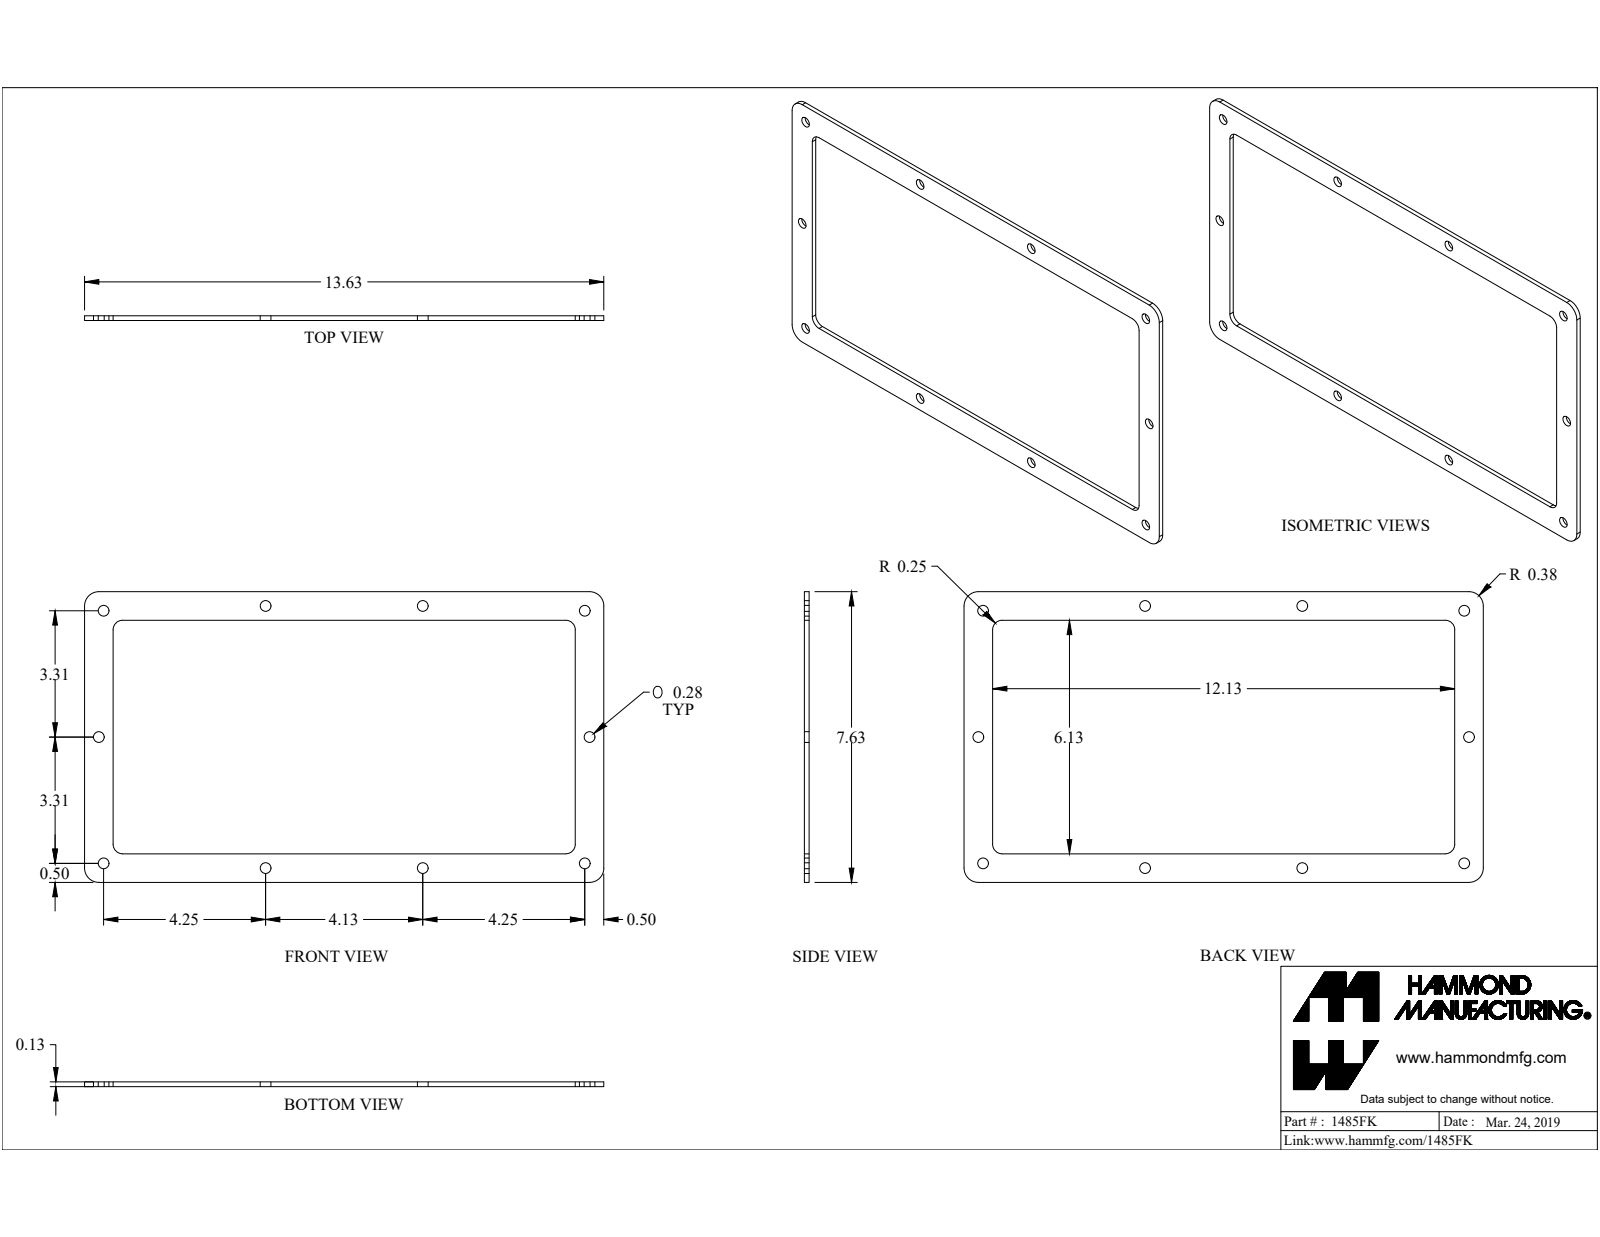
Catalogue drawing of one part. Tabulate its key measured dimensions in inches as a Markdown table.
| quantity | value |
| --- | --- |
| part name | 1485FK |
| STEP written by | SolidWorks 2019 (CONFIG_CONTROL_DESIGN) |
| units | inches |
| bodies | 1 solid, 28 faces (10 planar, 18 cylindrical, 0 other) |
| overall size | 13.625 × 7.625 × 0.125 |
| volume | 3.617 in³ |
| surface area | 68.72 in² |
| round holes (diameter × count) | 0.281 × 10 |
| partial cylindrical surfaces (radius × count) | 0.25 × 4, 0.375 × 4 |
| main face-to-face distances | 0.125, 0.75, 6.875, 7.625, 6.125, 12.875, 13.625, 12.125 |
| hole center spacings | 3.315, 4.252, 5.564, 7.976, 8.376, 9.169, 10.757, 13.173 |
